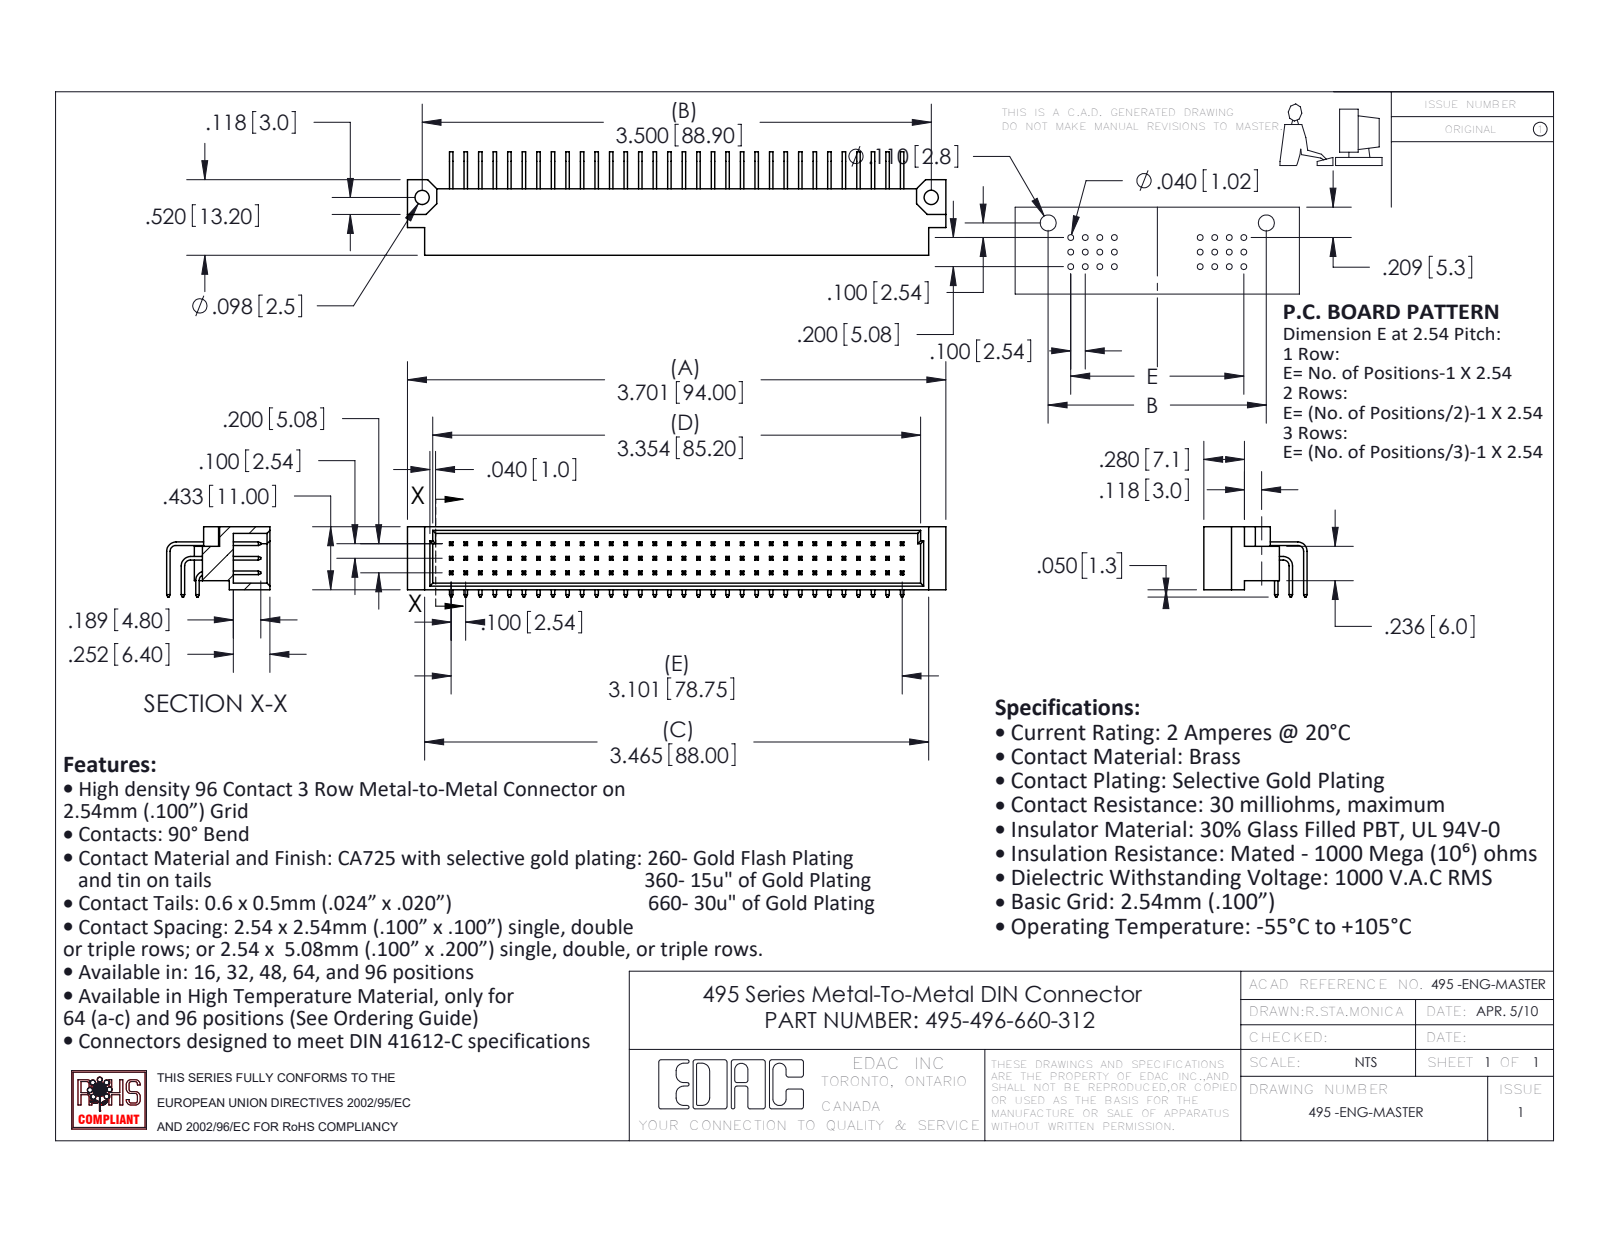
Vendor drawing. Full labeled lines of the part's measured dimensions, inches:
Part name (STEP PRODUCT): 495 Part_96; 495-290-1; 495-496-660-312; 495-290-2 (+1 more)
STEP written by: SolidWorks 2020 (AUTOMOTIVE_DESIGN)
Units: inches
Bodies: 97 solids, 2161 faces (1965 planar, 196 cylindrical, 0 other)
Overall size (bounding box): 3.701 × 0.711 × 0.483
Volume: 0.404 in³ · Surface area: 17.74 in²
Round holes (diameter × count): ⌀0.098 ×2
Partial cylindrical surfaces — rounded edges, fillets, slot ends (radius × count): R0.04 ×3, R0.065 ×3
Main face-to-face distances: 0.1, 0.024, 0.2, 0.205, 0.045, 0.388, 0.124, 0.076, 0.433, 0.343
Hole centre spacings: 3.5
